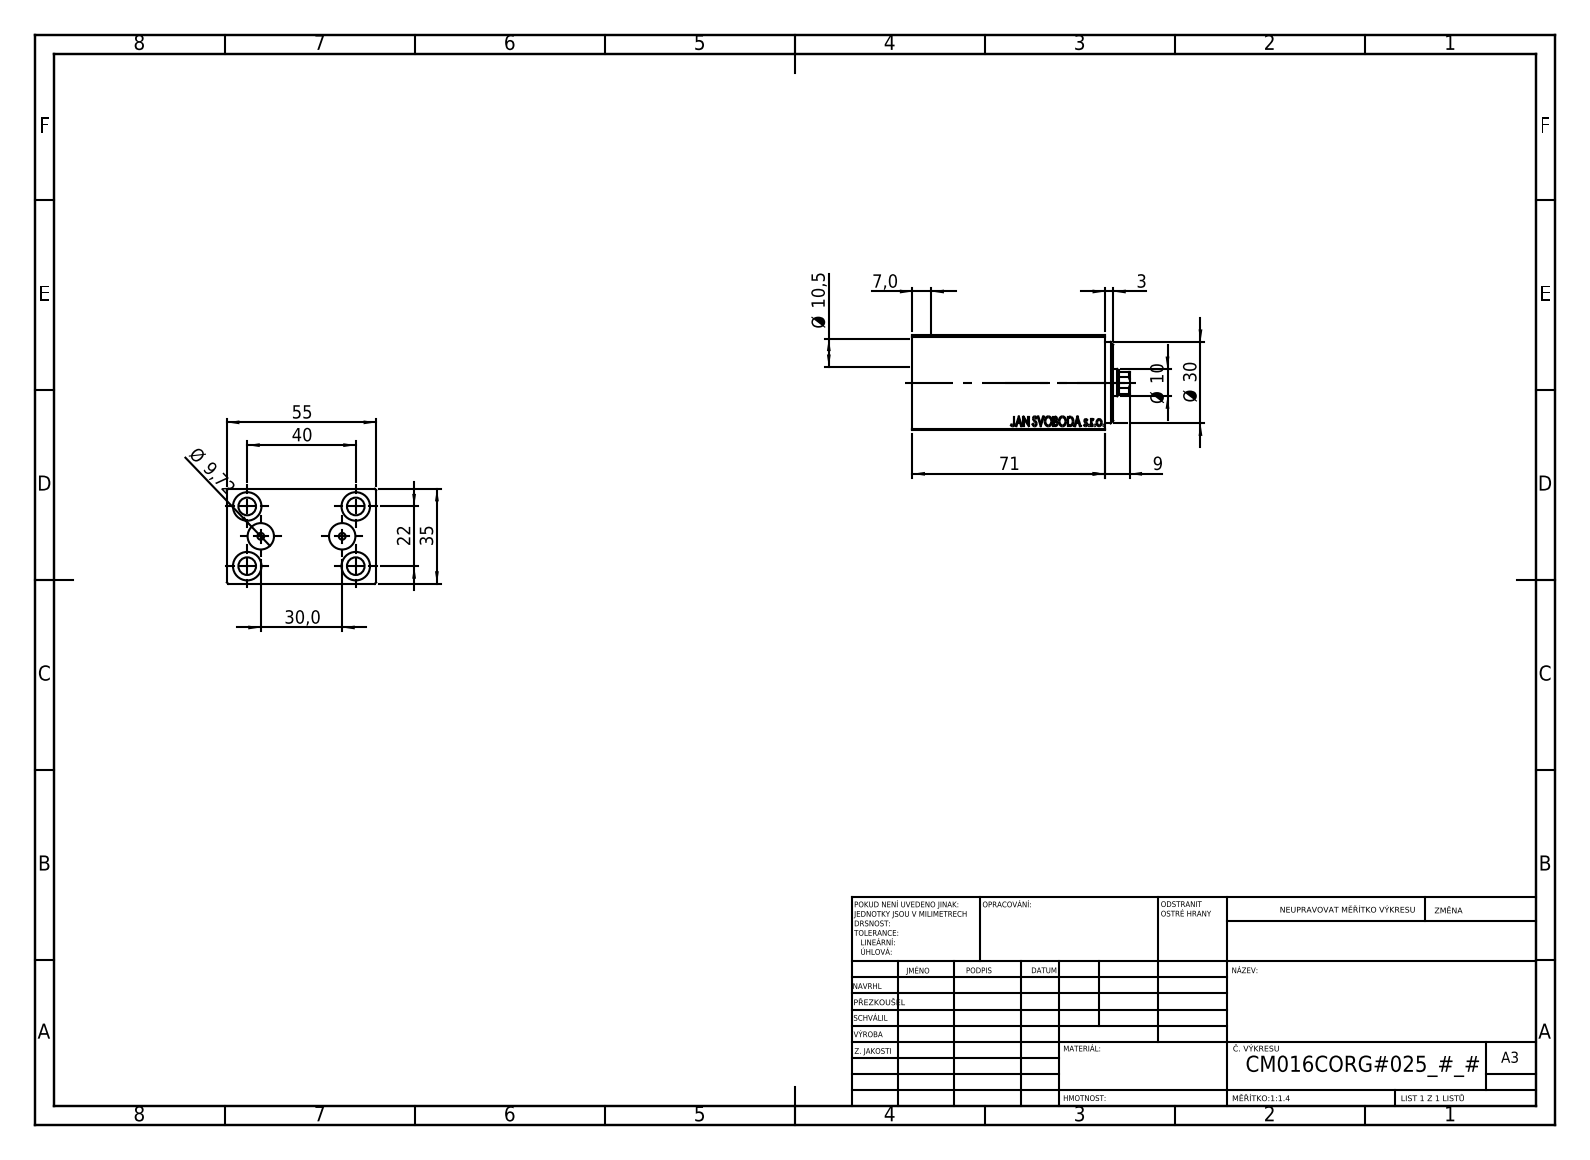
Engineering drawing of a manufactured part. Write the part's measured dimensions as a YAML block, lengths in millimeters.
part_name: "V450CM_C_VCP; V450CM_C_Body; V450CM_VC_B"
step_written_by: "SolidWorks 2019 (CONFIG_CONTROL_DESIGN)"
units: millimeters
bodies: {solids: 3, faces: 861, planar: 409, cylindrical: 58, other: 394}
overall_size: [80, 55, 35]
volume: 121226
surface_area: 33989
round_holes:
  - {diameter: 6.5, count: 4}
  - {diameter: 10.5, count: 4}
  - {diameter: 2.5, count: 2}
  - {diameter: 9.72, count: 2}
  - {diameter: 4.5, count: 1}
  - {diameter: 10, count: 1}
  - {diameter: 13.5, count: 1}
  - {diameter: 14.5, count: 1}
  - {diameter: 16, count: 1}
  - {diameter: 18, count: 1}
  - {diameter: 30, count: 1}
partial_cylinders:
  - {radius: 4.5, count: 1}
face_to_face_distances: [35, 55, 5, 66, 71, 2, 3, 64, 61, 8]
hole_center_spacings: [12.08, 22.83, 36.69, 15, 22, 40, 45.65, 30]
